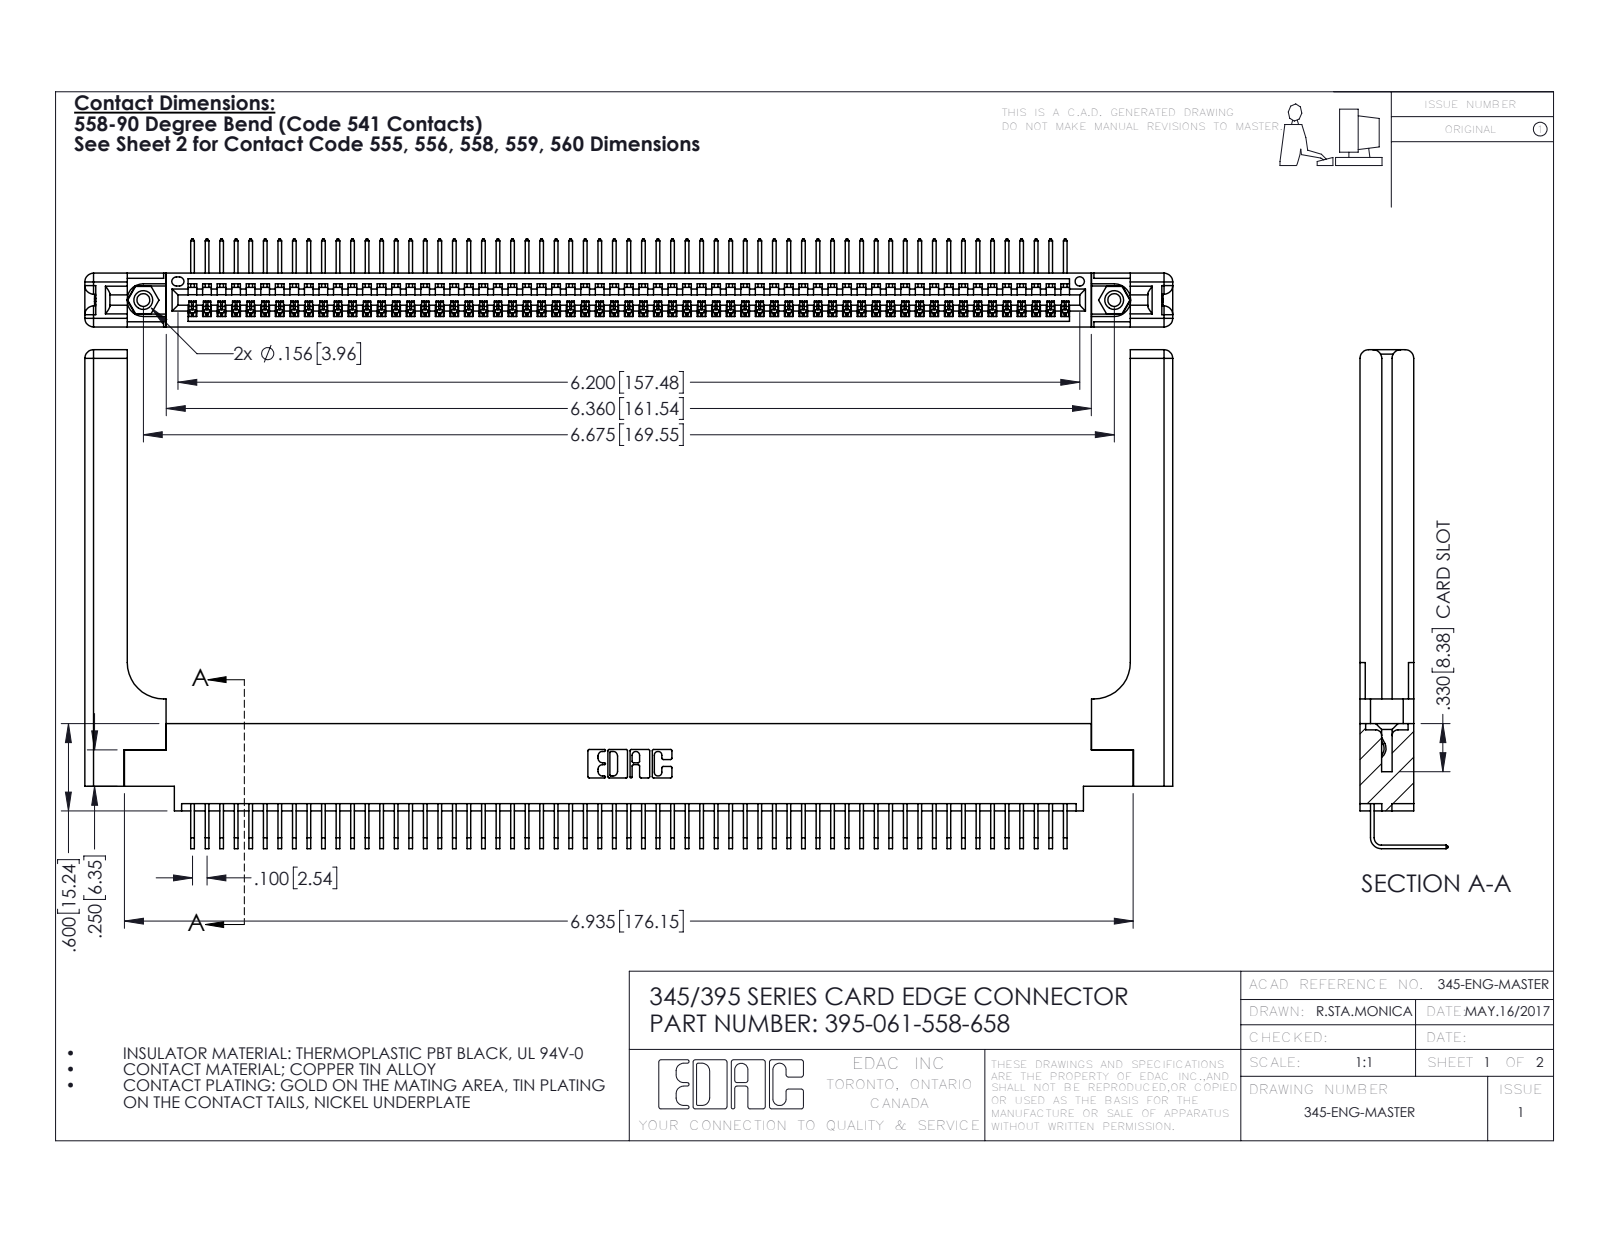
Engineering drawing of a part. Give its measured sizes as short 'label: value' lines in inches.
name: 345-220-058_345-220-058; 345-250-001_345-250-001-102; 395-061-558-658; 345 Part_0.170 Offset - 0.156 Dia-TH (+1 more)
written by: SolidWorks 2016 (CONFIG_CONTROL_DESIGN)
unit: in
bodies: 66 solids, 4046 faces (2794 planar, 1192 cylindrical, 60 other)
size: 7.479 × 3.429 × 0.605
volume: 1.635 in³; area: 48.34 in²
holes: 2× ⌀0.089, 2× ⌀0.125, 2× ⌀0.156, 1× ⌀0.064
bosses: 2× ⌀0.155
rounds: 122× R0.006, 22× R0.01, 16× R0.06, 6× R0.007, 6× R0.031, 3× R0.026, 2× R0.03, 2× R0.031
face distances: 0.072, 0.37, 0.298, 0.098, 0.272, 0.025, 0.2, 0.225, 0.148, 0.15
hole spacings: 0.27, 6.439, 6.675
